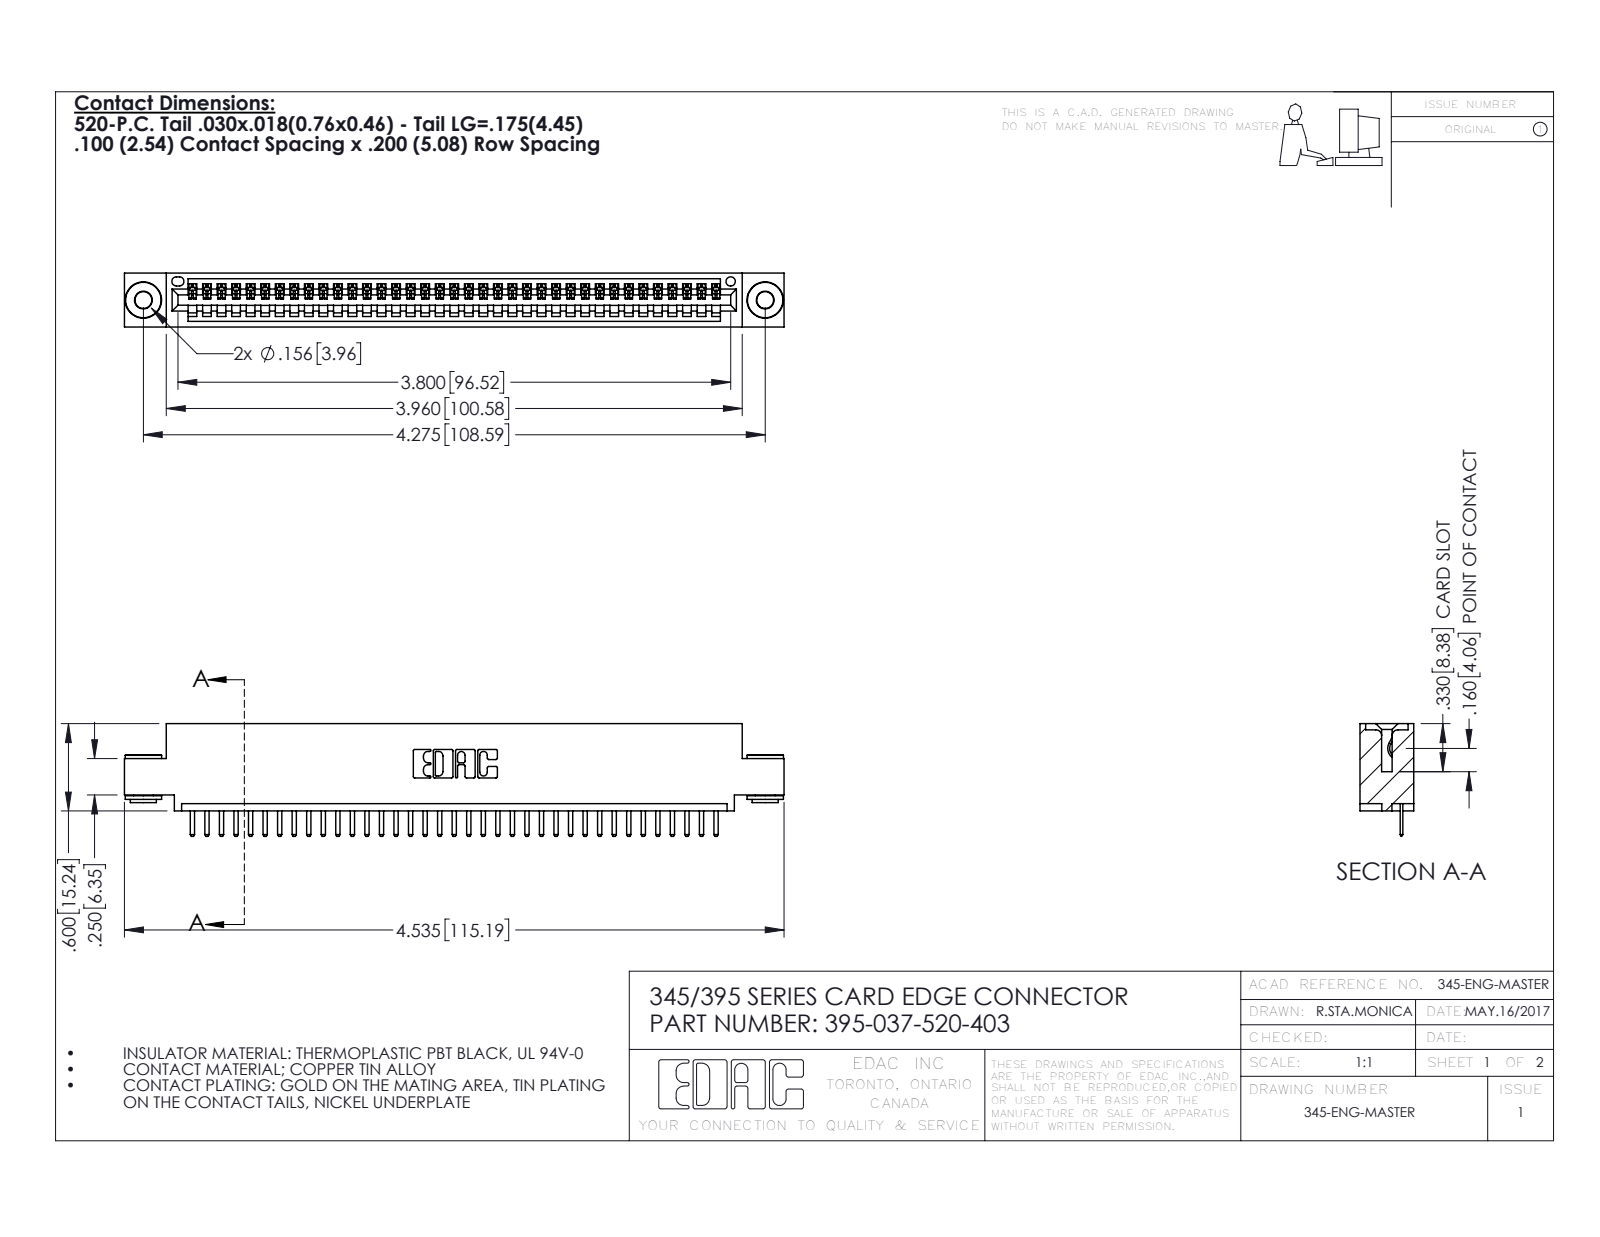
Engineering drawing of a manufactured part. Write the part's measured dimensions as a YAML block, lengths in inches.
part_name: "345 Part_0.110 Offset - 0.156 Dia-TH; 395-037-520-403; 345-250-002_345-250-002-102; 345-292-001_345-293-120"
step_written_by: "SolidWorks 2016 (CONFIG_CONTROL_DESIGN)"
units: inches
bodies: {solids: 40, faces: 2462, planar: 1648, cylindrical: 806, other: 8}
overall_size: [4.535, 0.775, 0.37]
volume: 0.655
surface_area: 21.94
round_holes:
  - {diameter: 0.116, count: 2}
  - {diameter: 0.156, count: 2}
  - {diameter: 0.064, count: 1}
round_bosses_or_shafts:
  - {diameter: 0.25, count: 2}
  - {diameter: 0.18, count: 2}
  - {diameter: 0.136, count: 2}
partial_cylinders:
  - {radius: 0.01, count: 76}
  - {radius: 0.006, count: 74}
  - {radius: 0.01, count: 22}
  - {radius: 0.007, count: 6}
  - {radius: 0.031, count: 6}
  - {radius: 0.026, count: 3}
  - {radius: 0.031, count: 2}
  - {radius: 0.04, count: 2}
face_to_face_distances: [0.072, 0.298, 0.37, 0.2, 0.025, 0.098, 0.272, 0.225, 0.072, 0.149]
hole_center_spacings: [0.27, 4.039, 4.275]
